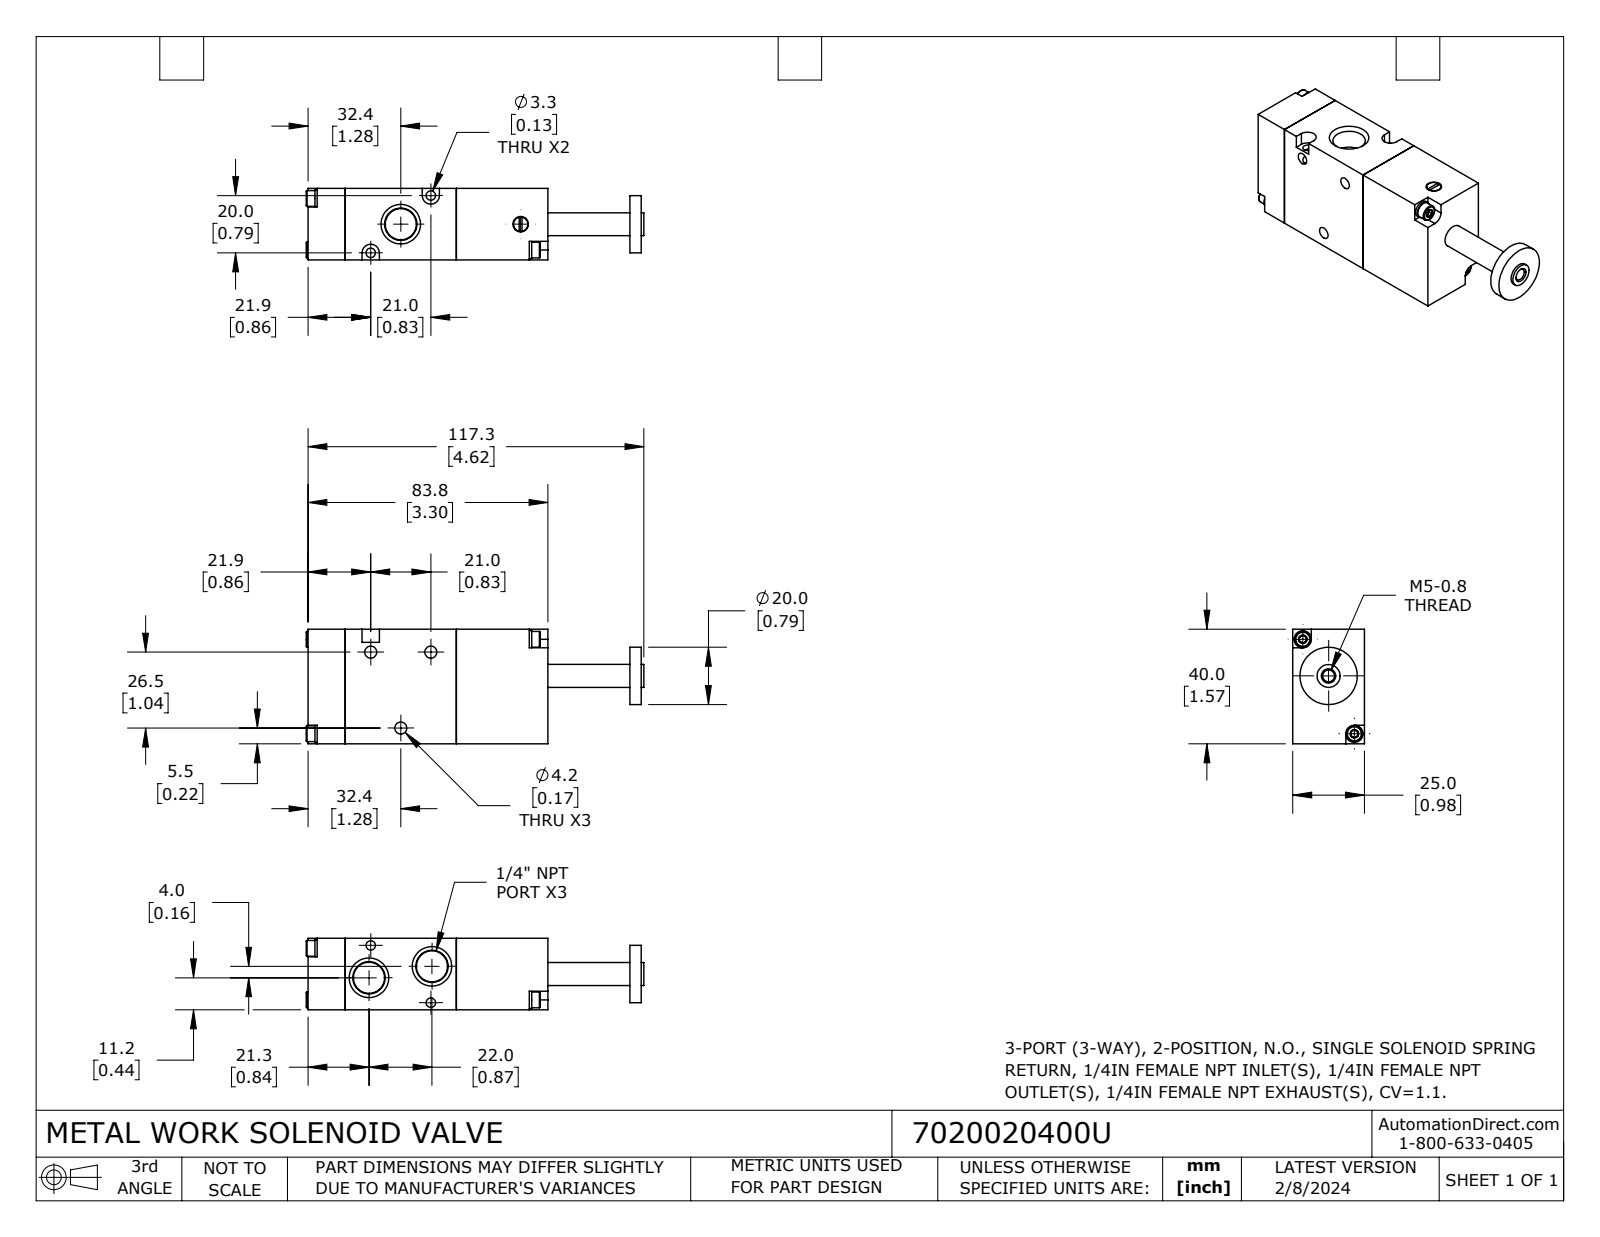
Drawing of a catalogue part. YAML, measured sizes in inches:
part_name: "7020020400U"
step_written_by: "SolidWorks 2023 (CONFIG_CONTROL_DESIGN)"
units: inches
bodies: {solids: 11, faces: 251, planar: 116, cylindrical: 65, other: 70}
overall_size: [4.642, 1.575, 0.984]
volume: 5.01
surface_area: 34.01
round_holes:
  - {diameter: 0.118, count: 4}
  - {diameter: 0.165, count: 3}
  - {diameter: 0.13, count: 2}
  - {diameter: 0.163, count: 1}
  - {diameter: 0.213, count: 1}
round_bosses_or_shafts:
  - {diameter: 0.236, count: 4}
  - {diameter: 0.217, count: 4}
  - {diameter: 0.787, count: 1}
  - {diameter: 0.315, count: 1}
  - {diameter: 0.197, count: 1}
partial_cylinders:
  - {radius: 0.118, count: 2}
face_to_face_distances: [0.984, 1.528, 1.575, 0.512, 2.039, 3.299, 2.787, 1.26, 0.311, 1.264]
hole_center_spacings: [0.616, 0.709, 0.87, 1.122, 1.299, 1.48, 0.827, 1.142]
